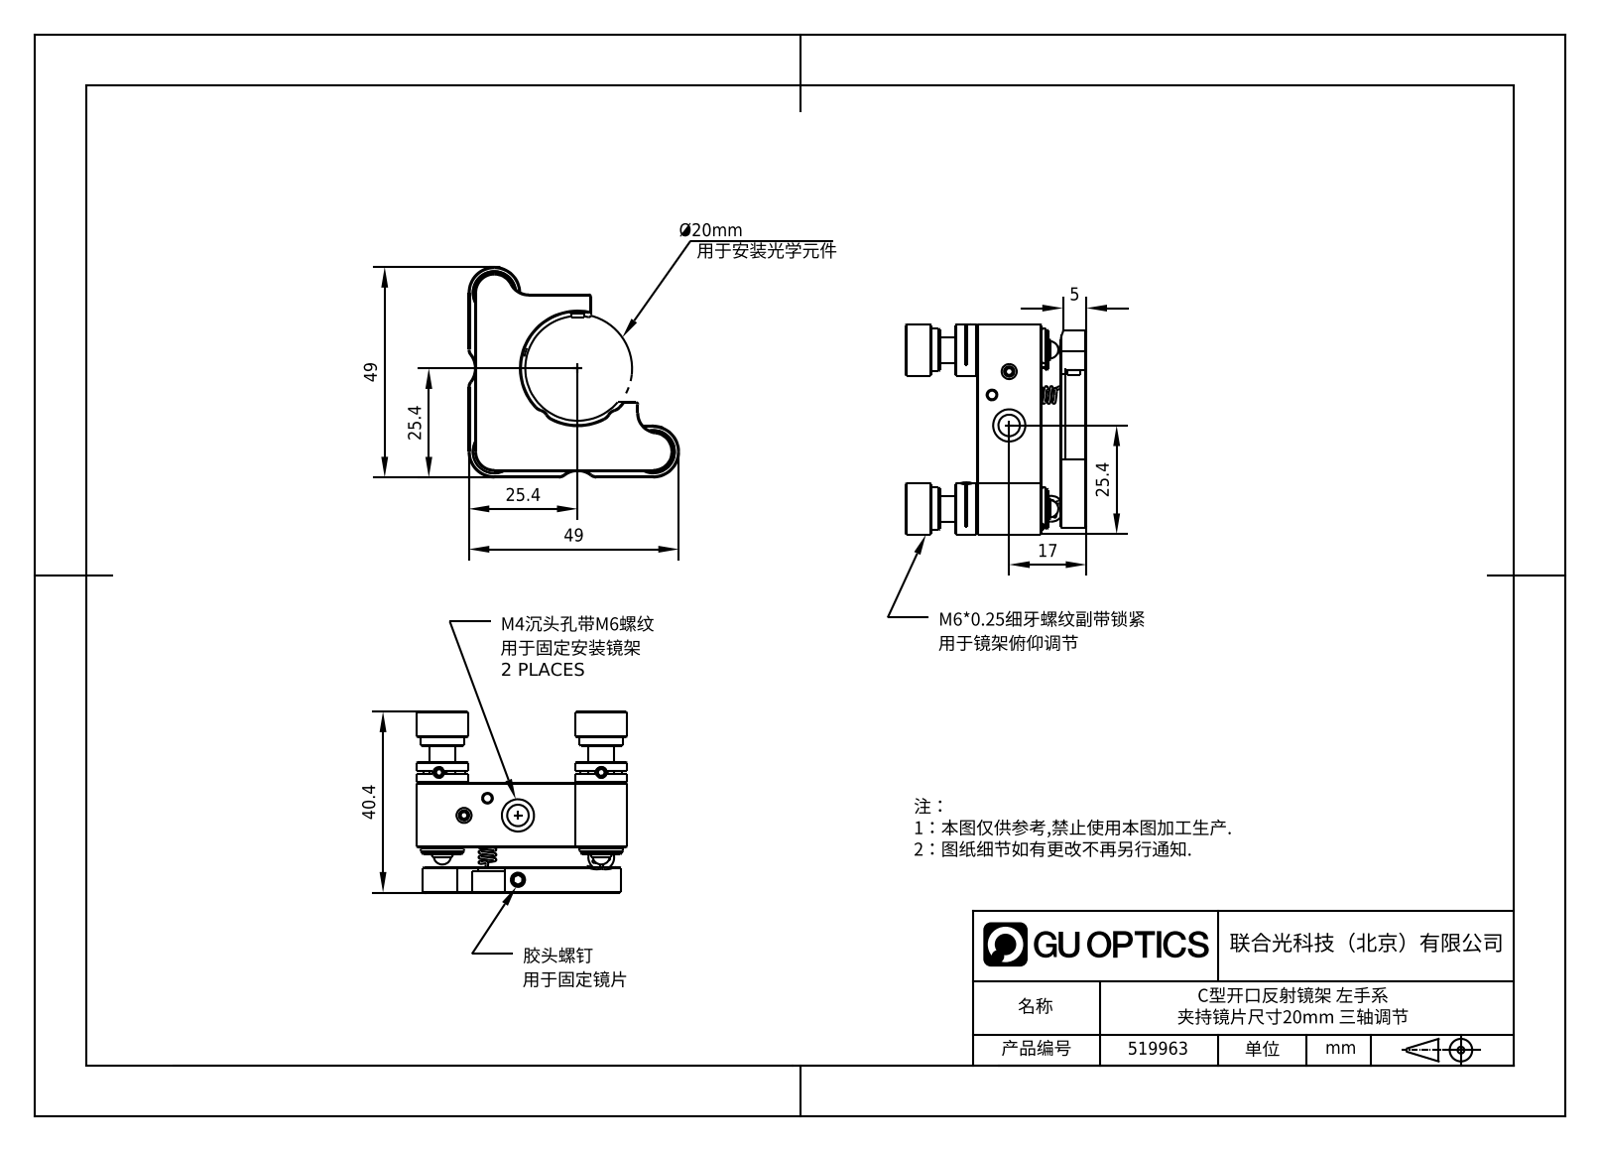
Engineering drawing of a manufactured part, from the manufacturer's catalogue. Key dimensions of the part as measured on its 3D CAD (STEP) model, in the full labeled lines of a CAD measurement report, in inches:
Part name (STEP PRODUCT): JC版，2.1.13.22，OMC-20L-3，20mmC型开口反射调整架，左手，3轴
STEP written by: SolidWorks 2023 (AUTOMOTIVE_DESIGN)
Units: inches
Bodies: 0 solids, 1336 faces (632 planar, 425 cylindrical, 279 other)
Overall size (bounding box): 2.028 × 2.028 × 1.614
Round holes (diameter × count): ⌀0.098 ×4, ⌀0.236 ×4, ⌀0.157 ×3, ⌀0.181 ×2, ⌀0.197 ×2, ⌀0.315 ×2, ⌀0.13 ×1, ⌀0.378 ×1
Round bosses / shafts (diameter × count): ⌀0.118 ×8, ⌀0.157 ×4, ⌀0.059 ×4, ⌀0.492 ×3, ⌀0.472 ×3, ⌀0.413 ×3, ⌀0.374 ×3, ⌀0.315 ×3
Partial cylindrical surfaces — rounded edges, fillets, slot ends (radius × count): R0.012 ×9, R0.031 ×8, R0.039 ×8, R0.098 ×5, R0.02 ×4, R0.049 ×4, R0.295 ×3, R0.122 ×2
Main face-to-face distances: 0.236, 0.965, 0.728, 0.138, 0.374, 0.591, 0.039, 0.089, 0.108, 0.453
Hole centre spacings: 0.197, 0.384, 0.404, 0.65, 1.033, 1.053, 1.128, 1.437
